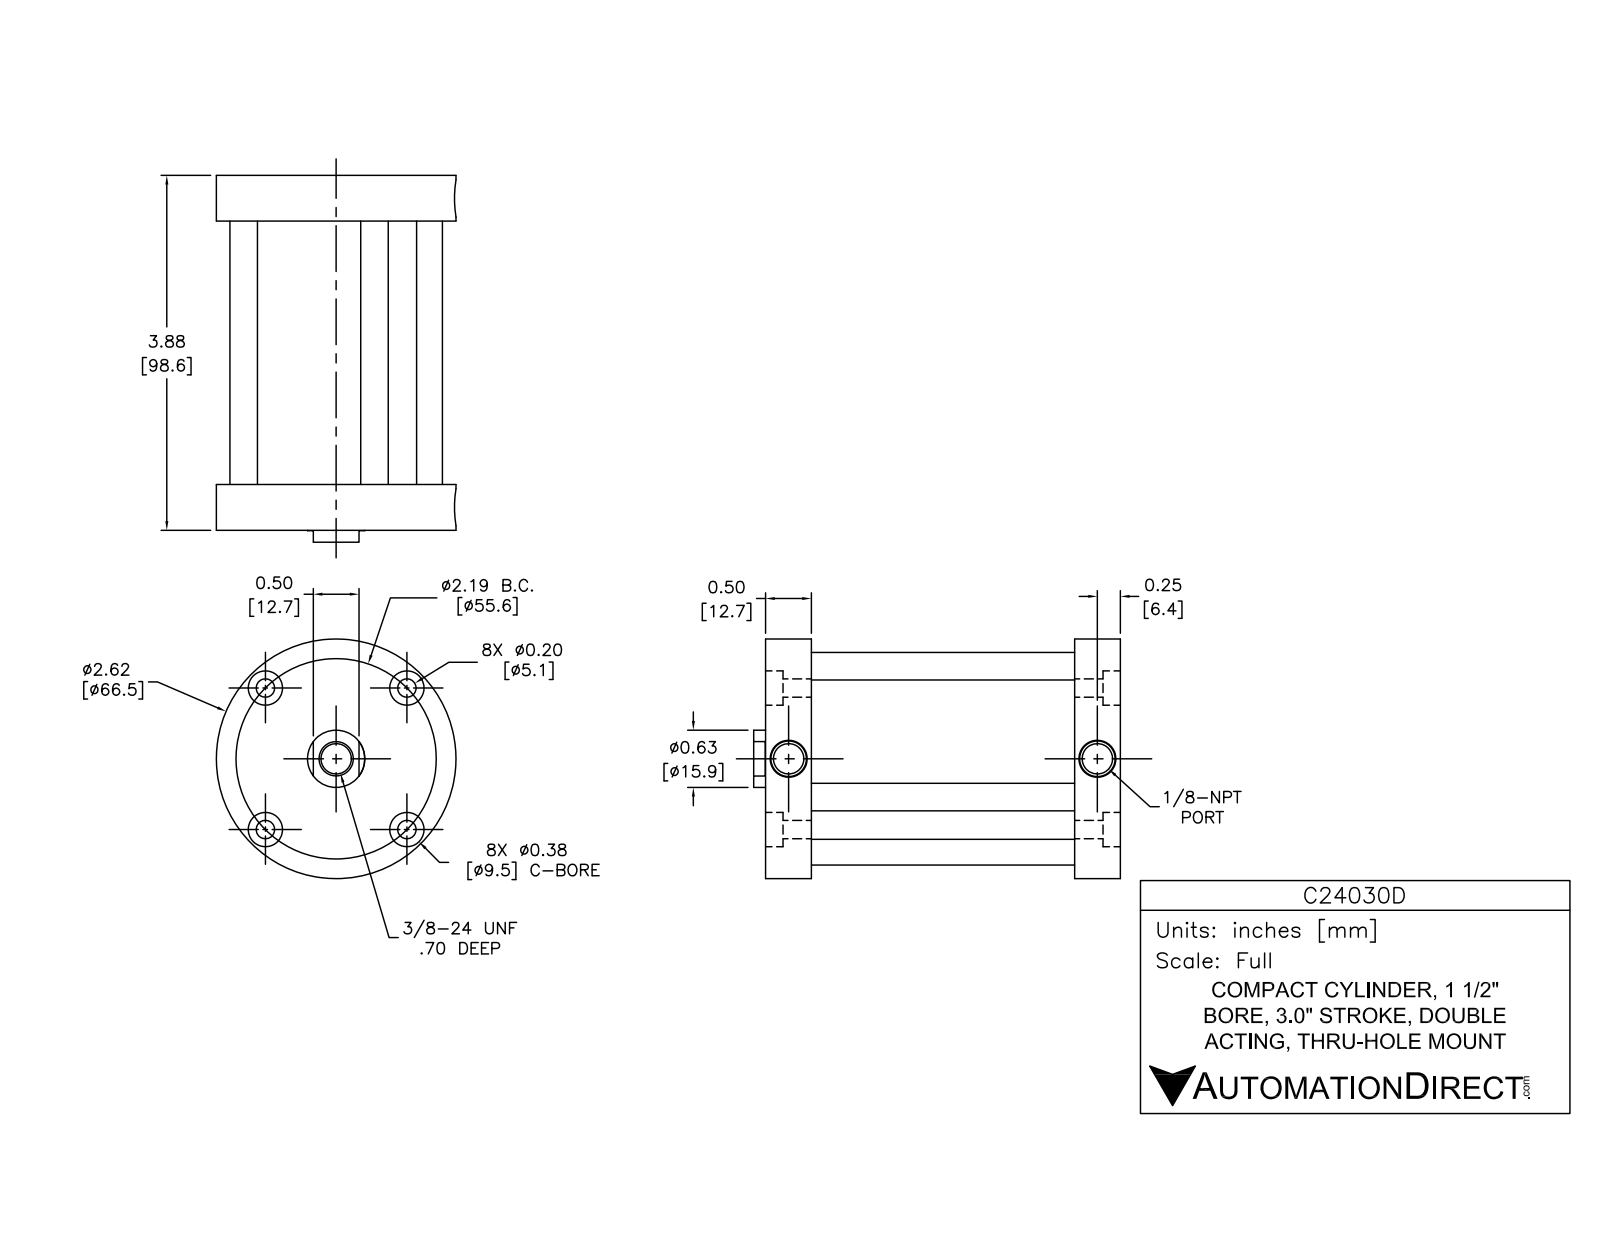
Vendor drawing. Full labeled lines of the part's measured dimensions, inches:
Part name (STEP PRODUCT): C24030D-FO1_BM_heads (2); C24030D-FO1_BM_tube; C24030D-rod_part; C24030D-FO1_BM_heads (+3 more)
STEP written by: SolidWorks 2014 (AUTOMOTIVE_DESIGN)
Units: inches
Bodies: 9 solids, 165 faces (49 planar, 98 cylindrical, 18 other)
Overall size (bounding box): 4.01 × 2.62 × 2.62
Volume: 7.632 in³ · Surface area: 99.17 in²
Round holes (diameter × count): ⌀0.2 ×4, ⌀0.218 ×4, ⌀0.343 ×4, ⌀0.125 ×2, ⌀0.33 ×1, ⌀0.63 ×1, ⌀0.632 ×1, ⌀1.503 ×1, ⌀1.563 ×1
Round bosses / shafts (diameter × count): ⌀0.4 ×4, ⌀2.62 ×1
Main face-to-face distances: 0.5, 3.38, 0.282, 3.598, 3.098, 0.218, 3.88, 2.88, 3.316, 0.598
Hole centre spacings: 1.095, 1.549, 0.428, 1.217, 1.821, 2.148, 2.19, 2.191
